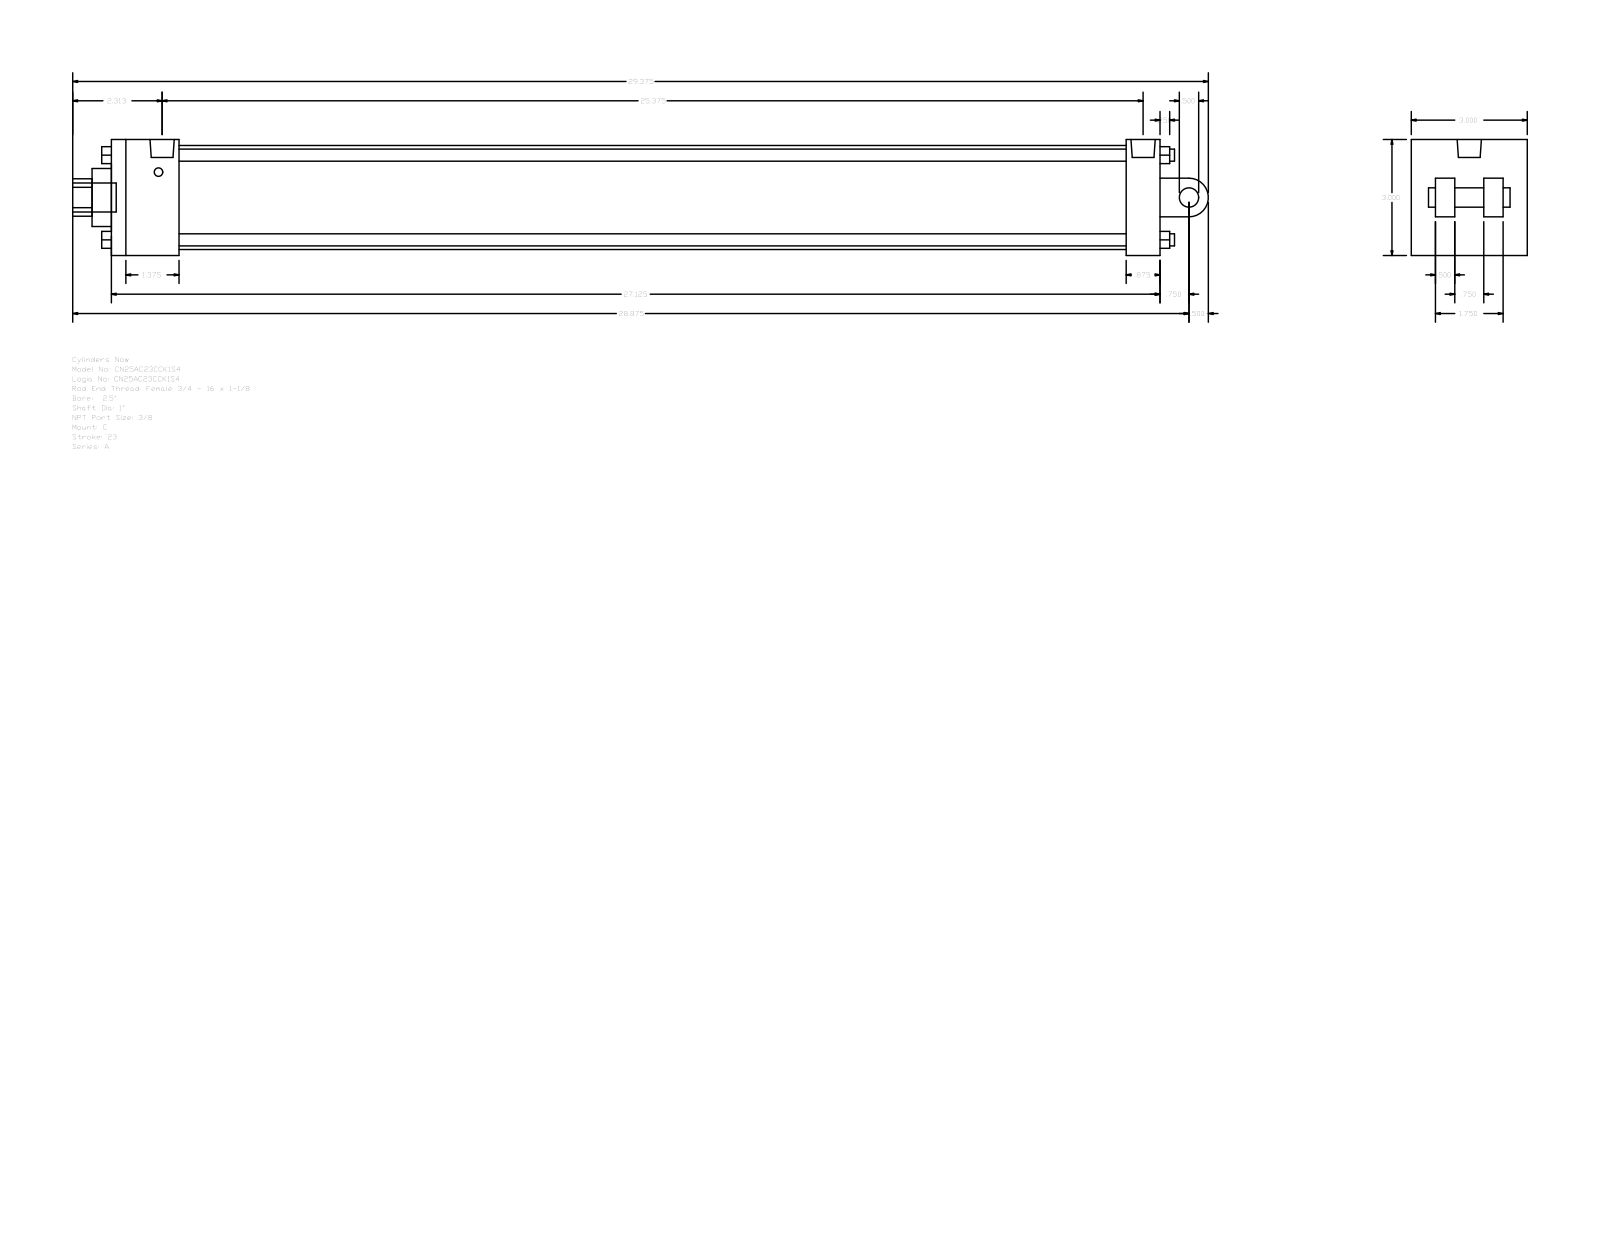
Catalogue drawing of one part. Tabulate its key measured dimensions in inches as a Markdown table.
| quantity | value |
| --- | --- |
| part name | A_C__0250_1 |
| STEP written by | GSSL Pune (CONFIG_CONTROL_DESIGN) |
| units | inches |
| bodies | 0 solids, 135 faces (102 planar, 33 cylindrical, 0 other) |
| overall size | 29.375 × 3 × 3 |
| round holes (diameter × count) | 0.219 × 2, 0.627 × 1, 1 × 1, 1.5 × 1, 2.69 × 1 |
| round bosses / shafts (diameter × count) | 0.313 × 4, 0.219 × 2, 0.75 × 1, 0.627 × 1, 0.5 × 1 |
| partial cylindrical surfaces (radius × count) | 0.484 × 1, 0.5 × 1 |
| main face-to-face distances | 3, 27.125, 0.5, 1.75, 26.25, 24.5, 25.375, 0.875, 0.625, 1 |
| hole center spacings | 0.094 |
